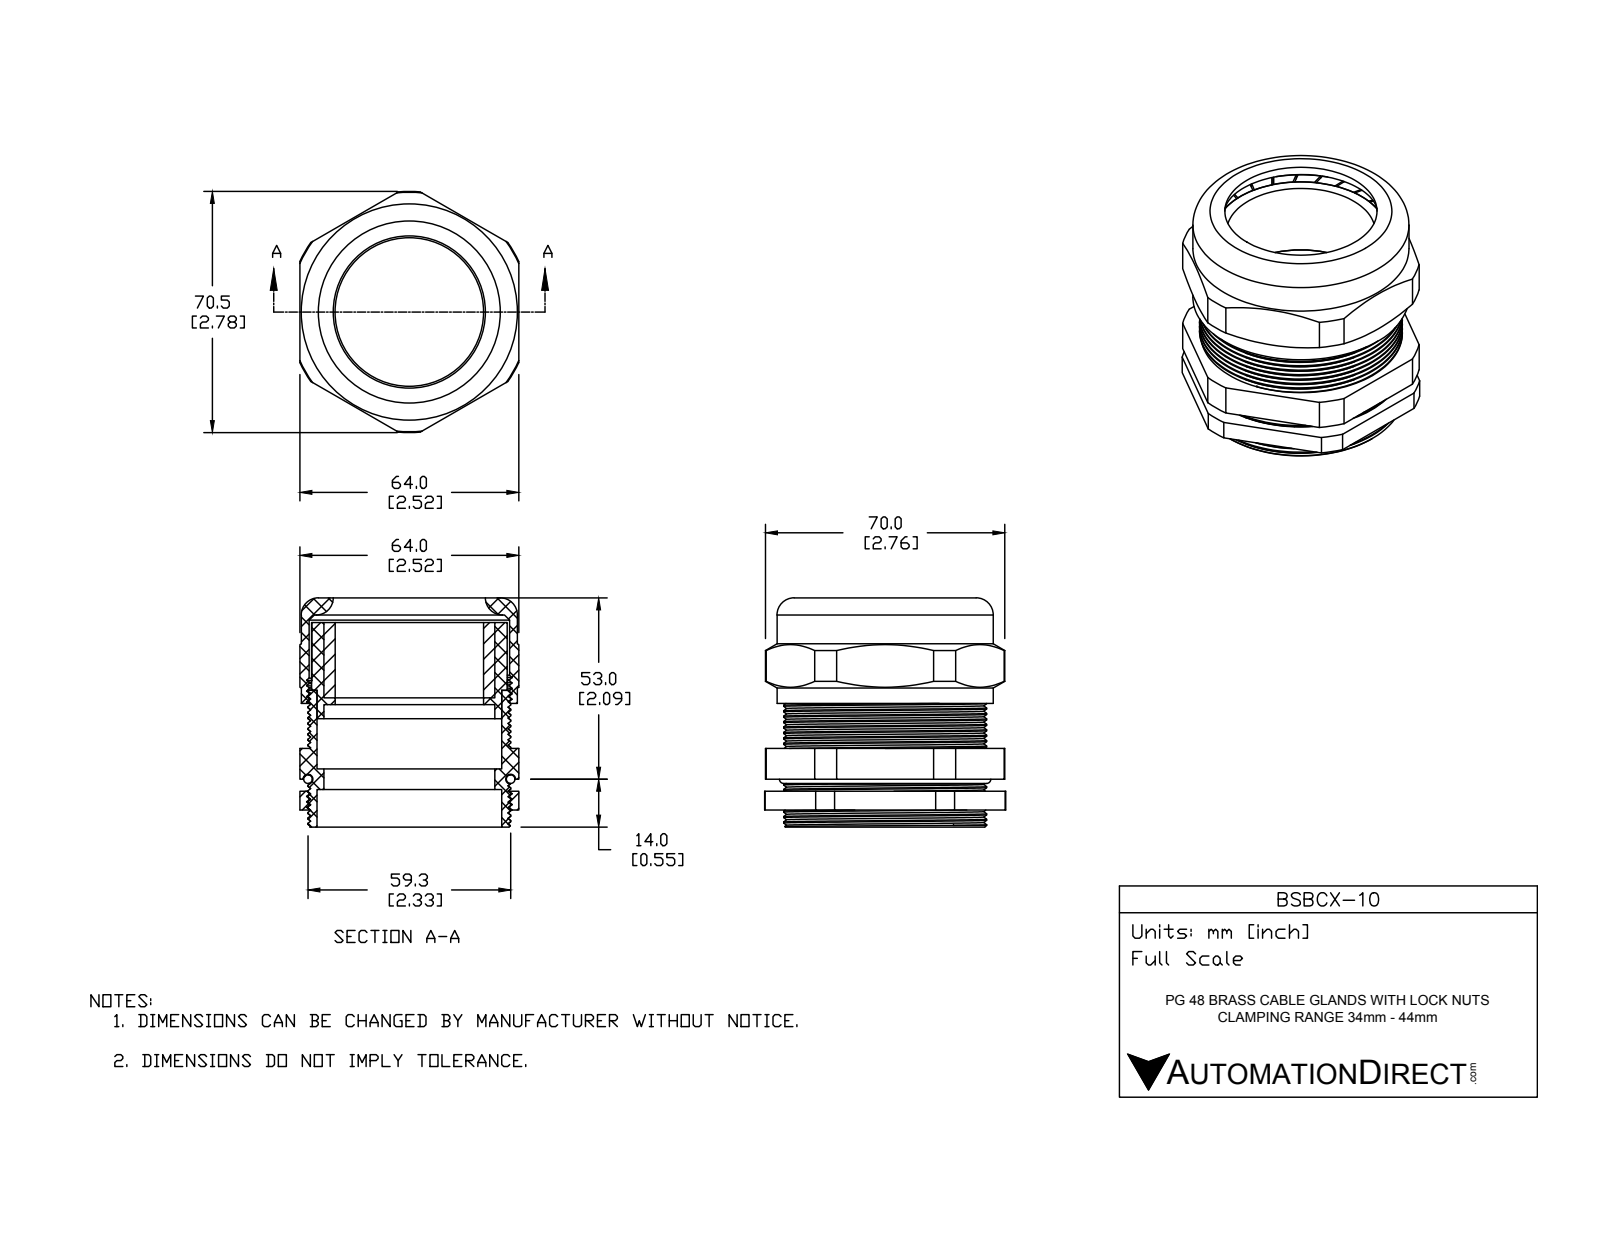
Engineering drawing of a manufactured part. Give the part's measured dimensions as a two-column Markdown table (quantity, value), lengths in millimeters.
| quantity | value |
| --- | --- |
| part name | BSBCX-10 |
| STEP written by | SolidWorks 2015 (CONFIG_CONTROL_DESIGN) |
| units | millimeters |
| bodies | 6 solids, 268 faces (137 planar, 102 cylindrical, 29 other) |
| overall size | 70.5 × 67 × 64 |
| volume | 76 821 mm³ |
| surface area | 62 892 mm² |
| round holes (diameter × count) | 43.42 × 1, 50 × 1, 54 × 1, 58.63 × 1 |
| round bosses / shafts (diameter × count) | 63.2 × 1, 59.3 × 1, 57.2 × 1 |
| partial cylindrical surfaces (radius × count) | 35 × 1, 35.25 × 1 |
| main face-to-face distances | 64, 0.5, 17, 22, 6, 9, 14.8, 36.8, 2.2, 62 |
